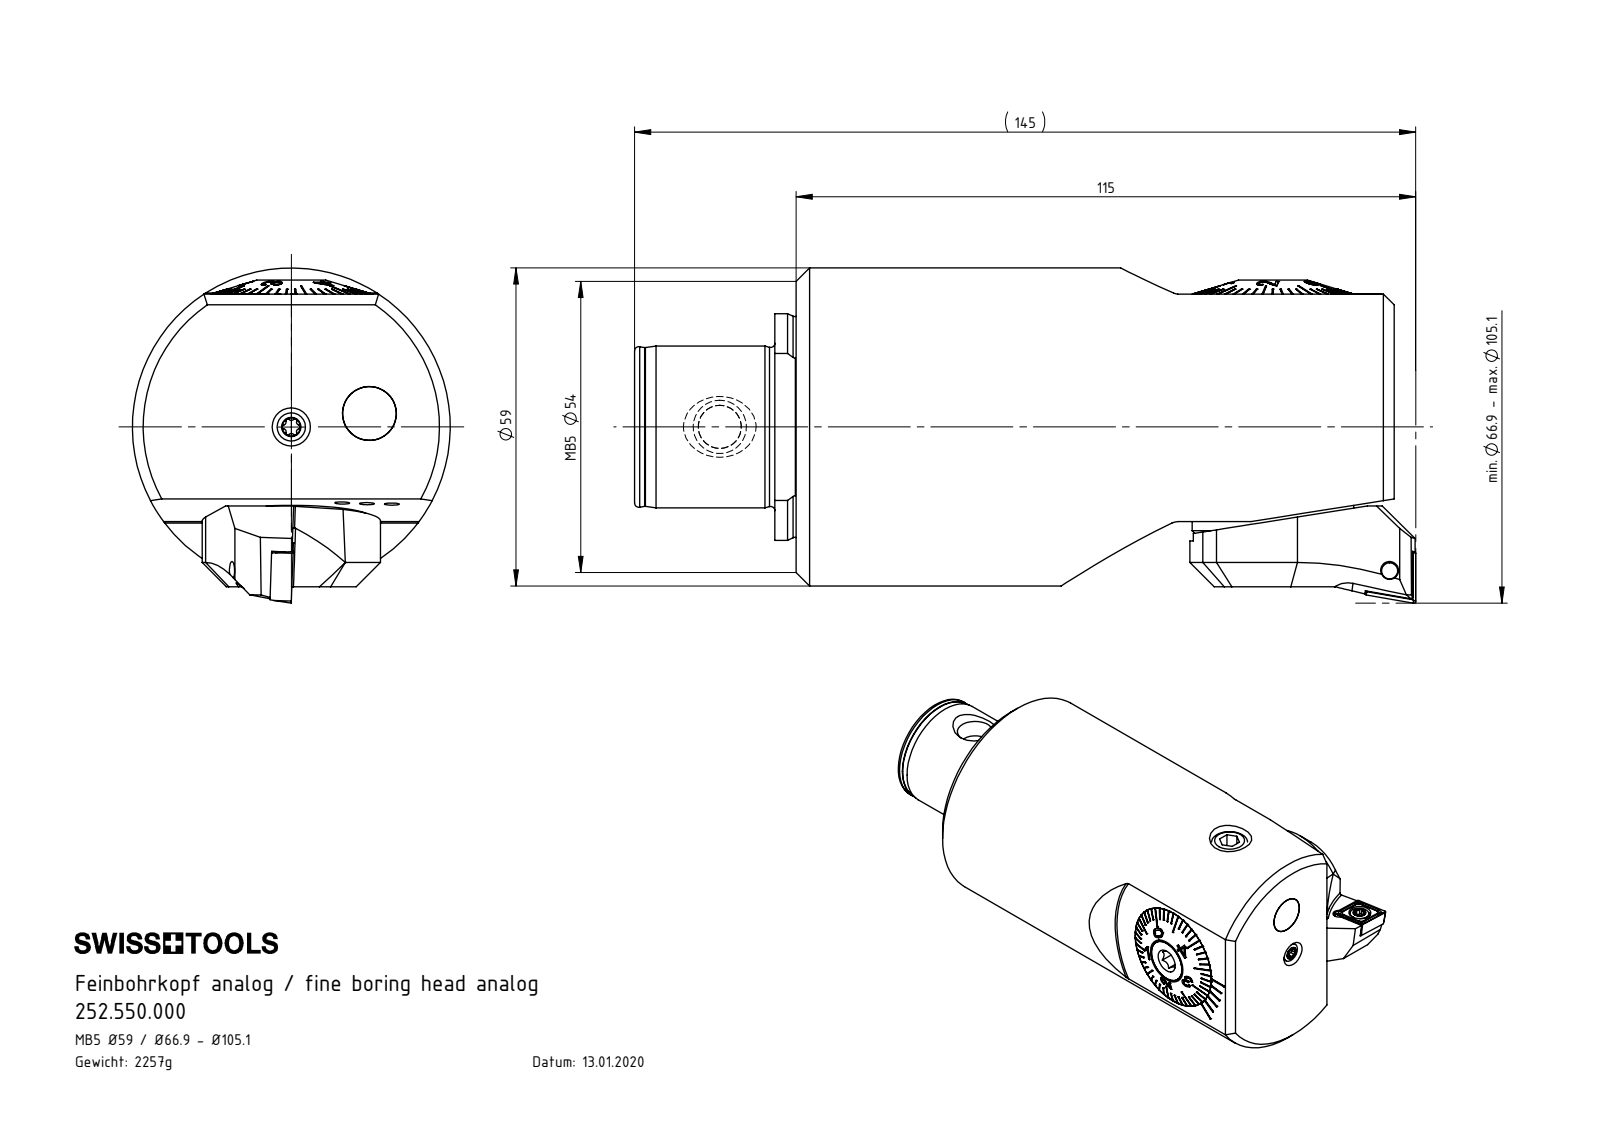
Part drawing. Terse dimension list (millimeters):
name: A55-BG2.011.016_D; F55-BG1.012.012_A; DIN 7984 - M10 x 16; F55-BG2.014.015_B_Fertig mit Gewinde (+8 more)
written by: SolidWorks 2017 (CONFIG_CONTROL_DESIGN)
unit: mm
bodies: 13 solids, 720 faces (303 planar, 136 cylindrical, 281 other)
size: 141 × 59.16 × 59
volume: 289 844 mm³; area: 51 883 mm²
holes: 3× ⌀2.5, 3× ⌀4.2, 3× ⌀8.5, 2× ⌀3.3, 2× ⌀8, 1× ⌀5, 1× ⌀10, 1× ⌀11.4, 1× ⌀12, 1× ⌀12.4, 1× ⌀13, 1× ⌀14
bosses: 2× ⌀30, 2× ⌀10, 1× ⌀59, 1× ⌀29.98, 1× ⌀29.9, 1× ⌀25, 1× ⌀18, 1× ⌀16
rounds: 6× R0.34, 6× R0.59, 6× R2.5, 4× R2, 3× R3.2, 2× R0.5, 1× R1, 1× R3.5
face distances: 111, 42.2, 2.81, 38.5, 30, 141, 35.69, 6.51, 41, 2.5
hole spacings: 14.71, 17.33, 102.73, 117.41
